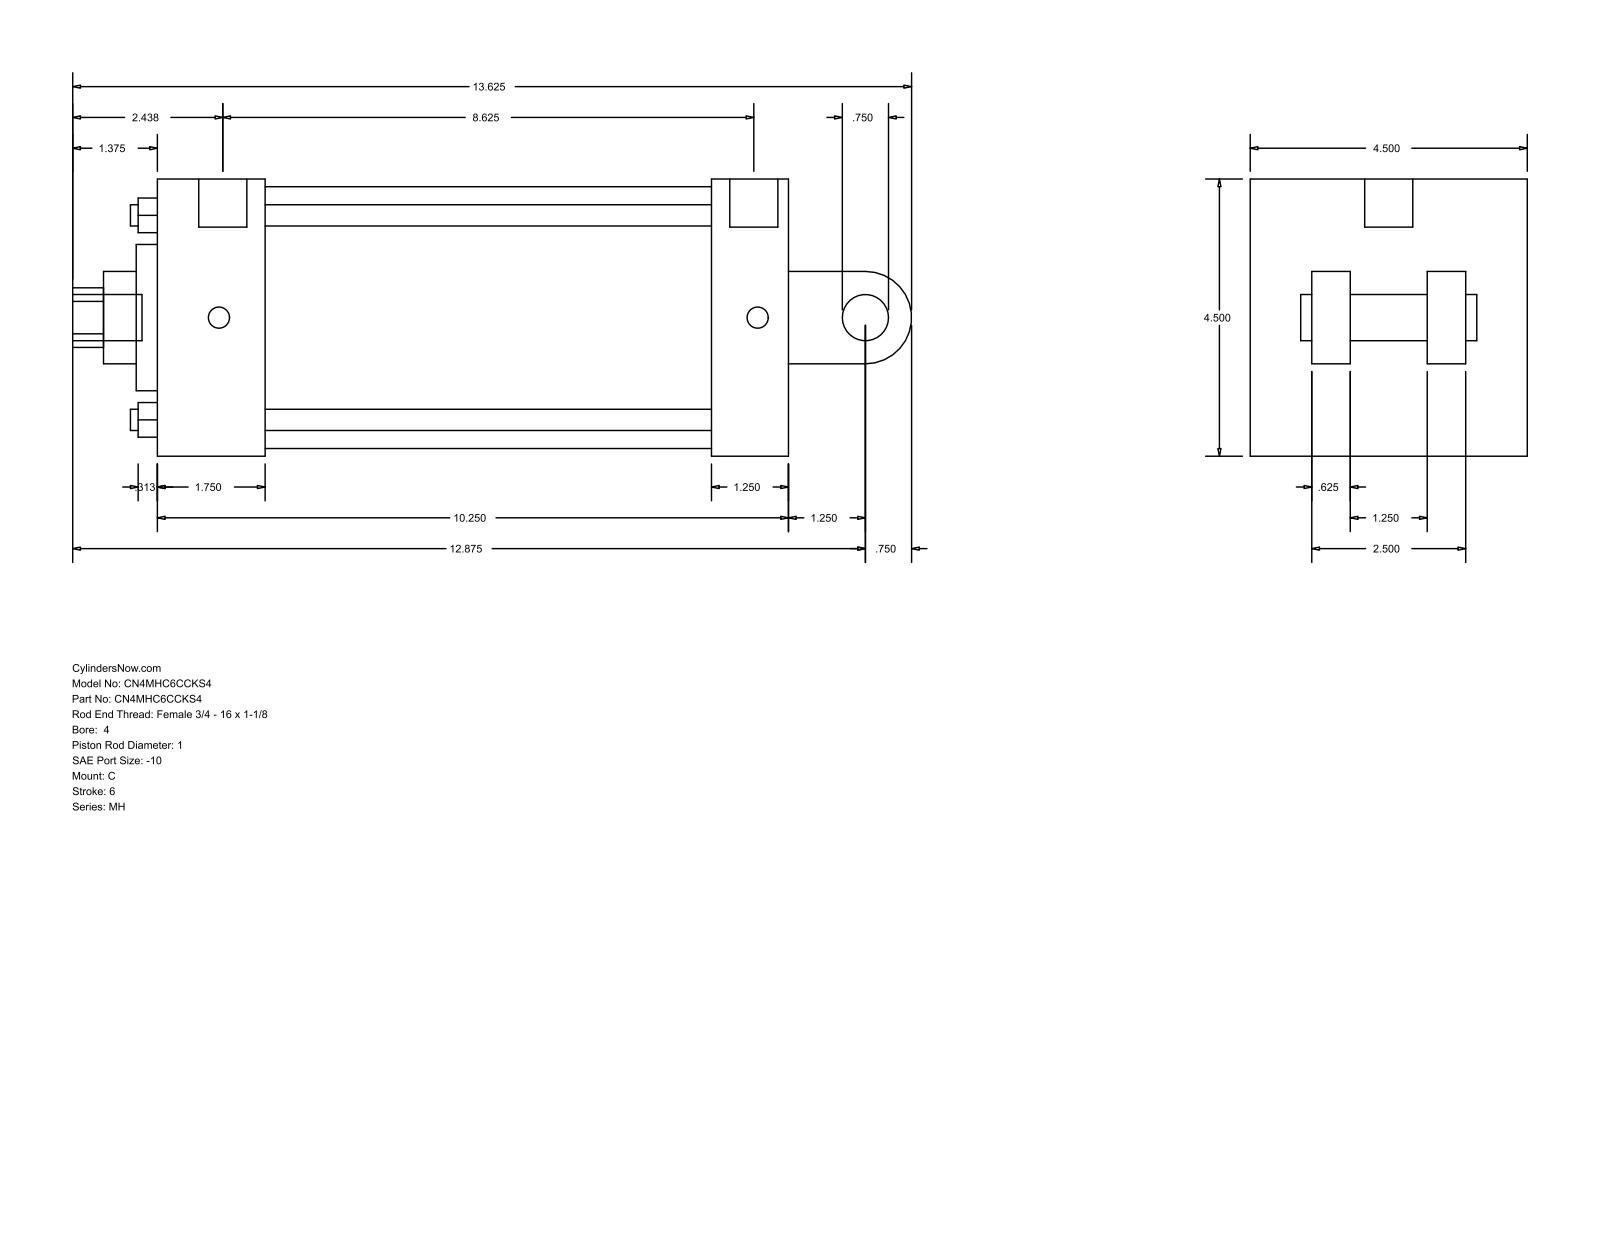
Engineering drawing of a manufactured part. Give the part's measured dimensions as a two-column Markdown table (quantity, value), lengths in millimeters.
| quantity | value |
| --- | --- |
| part name | MH_C__0400_1 |
| STEP written by | GSSL Pune (CONFIG_CONTROL_DESIGN) |
| units | millimeters |
| bodies | 0 solids, 101 faces (71 planar, 30 cylindrical, 0 other) |
| overall size | 346.07 × 114.3 × 114.3 |
| round holes (diameter × count) | 8.76 × 4, 8.73 × 2, 19.84 × 1, 25.4 × 1, 38.1 × 1, 60.33 × 1, 107.95 × 1 |
| round bosses / shafts (diameter × count) | 19.05 × 2, 8.73 × 2, 19.84 × 1 |
| partial cylindrical surfaces (radius × count) | 12.29 × 1, 19.05 × 1 |
| main face-to-face distances | 114.3, 260.35, 44.46, 228.6, 184.14, 215.89, 31.75, 73.03, 15.87, 47.63 |
| hole center spacings | 59.62, 84.32, 119.25, 1.58 |
